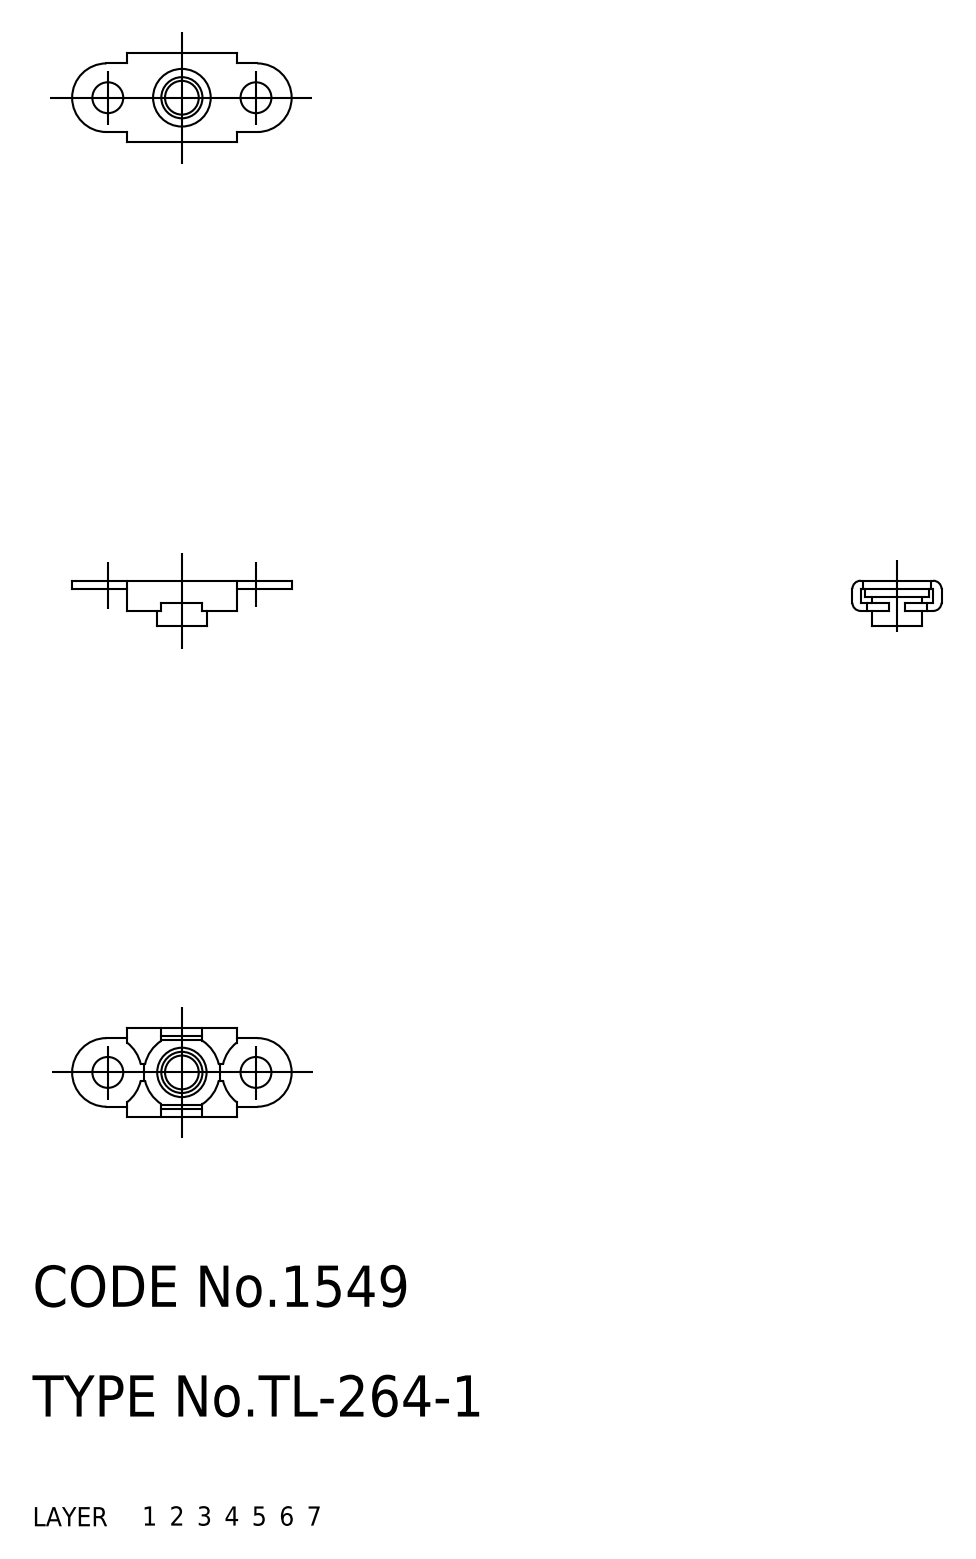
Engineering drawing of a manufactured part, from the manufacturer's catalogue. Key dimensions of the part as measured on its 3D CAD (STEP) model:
Part name (STEP PRODUCT): nut; housing; TL_264_1_1858_36
STEP written by: CADfix (AUTOMOTIVE_DESIGN)
Units: millimetres
Bodies: 2 solids, 75 faces (0 planar, 0 cylindrical, 75 other)
Overall size (bounding box): 16 × 6.5 × 3.3
Volume: 76 mm³ · Surface area: 346 mm²
